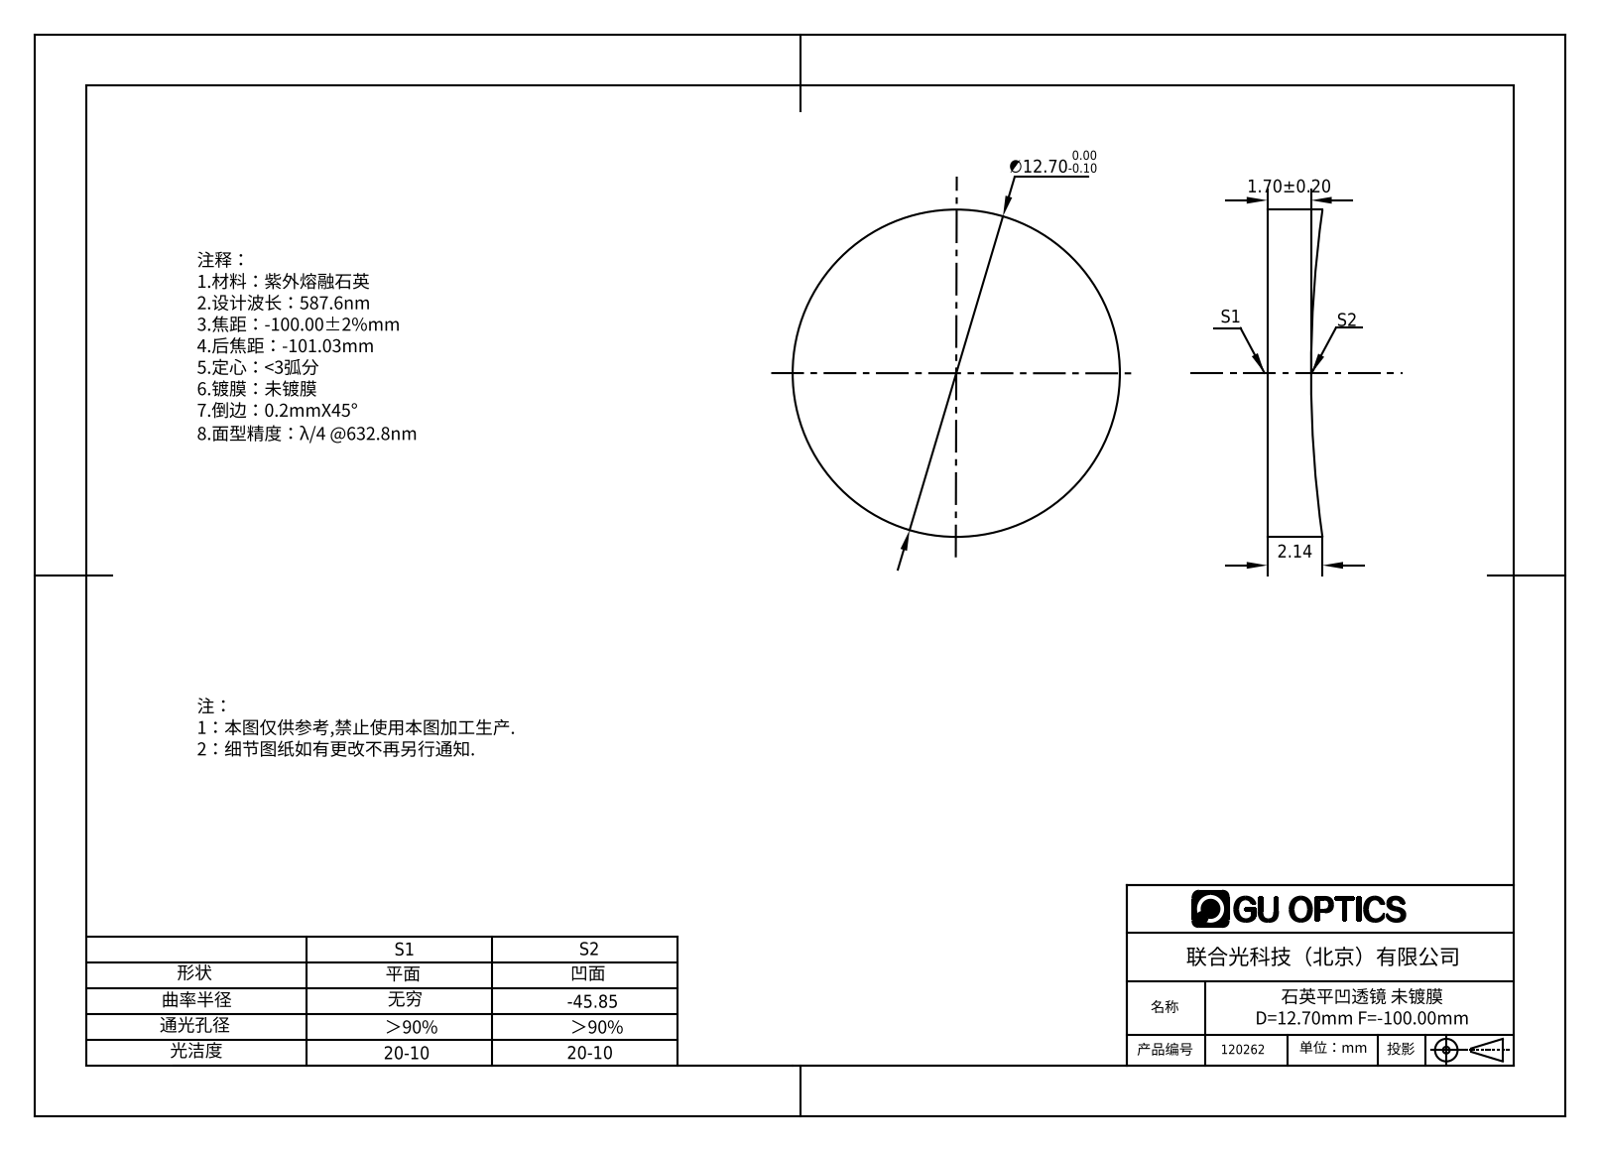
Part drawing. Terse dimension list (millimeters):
name: 120262
written by: SolidWorks 2016 (AUTOMOTIVE_DESIGN)
unit: mm
bodies: 1 solid, 5 faces (1 planar, 2 cylindrical, 2 other)
size: 12.7 × 12.7 × 2.14
volume: 243 mm³; area: 339 mm²
bosses: 1× ⌀12.7
